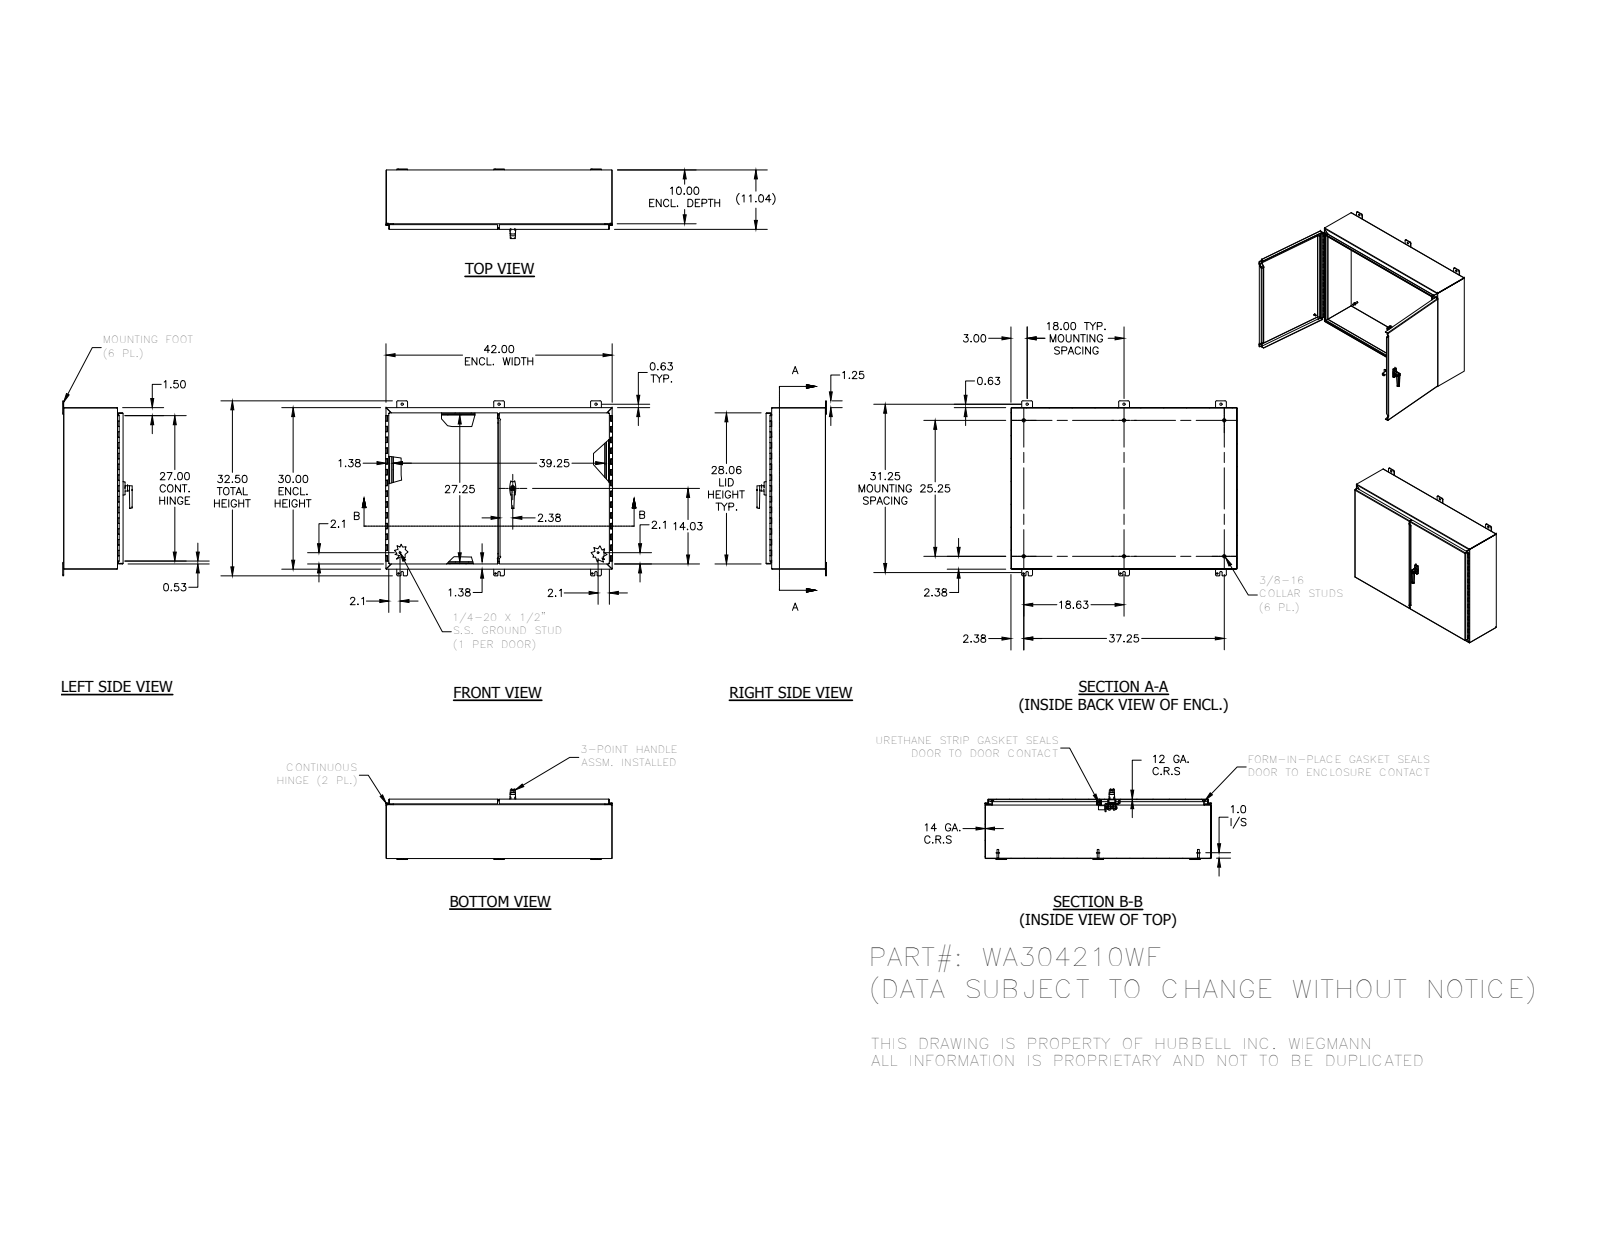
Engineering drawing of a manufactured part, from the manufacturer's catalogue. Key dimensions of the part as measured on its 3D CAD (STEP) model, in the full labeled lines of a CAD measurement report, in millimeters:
Part name (STEP PRODUCT): WA304210WF; WA304210WFLRS; 34840; WA304210WFBTB (+8 more)
STEP written by: Autodesk Inventor 2012 (AUTOMOTIVE_DESIGN)
Units: millimetres
Bodies: 60 solids, 2548 faces (1400 planar, 658 cylindrical, 490 other)
Overall size (bounding box): 1070.6 × 825.5 × 328.1
Volume: 6 686 000 mm³ · Surface area: 6 183 000 mm²
Round holes (diameter × count): ⌀7 ×8, ⌀2.1 ×6, ⌀8 ×6, ⌀11.1 ×6, ⌀5.1 ×4, ⌀3.2 ×2, ⌀4 ×2, ⌀6.1 ×2, ⌀6.4 ×2, ⌀6.4 ×2, ⌀10.2 ×2, ⌀10.3 ×2
Round bosses / shafts (diameter × count): ⌀4 ×7, ⌀15.9 ×6, ⌀8.4 ×6, ⌀6.4 ×4, ⌀2.9 ×4, ⌀25.4 ×2, ⌀14.3 ×2, ⌀13.4 ×2
Partial cylindrical surfaces — rounded edges, fillets, slot ends (radius × count): R0.8 ×28, R6.4 ×24, R0.2 ×22, R0.4 ×22, R2.7 ×17, R0.3 ×16, R1.3 ×14, R3.2 ×12
Main face-to-face distances: 1.9, 2.4, 277.9, 276, 280.3, 278.4, 760.1, 1064.9, 758.2, 762
Hole centre spacings: 457.2, 888.6, 7.4, 40.5, 762, 5.1, 441.2, 476
